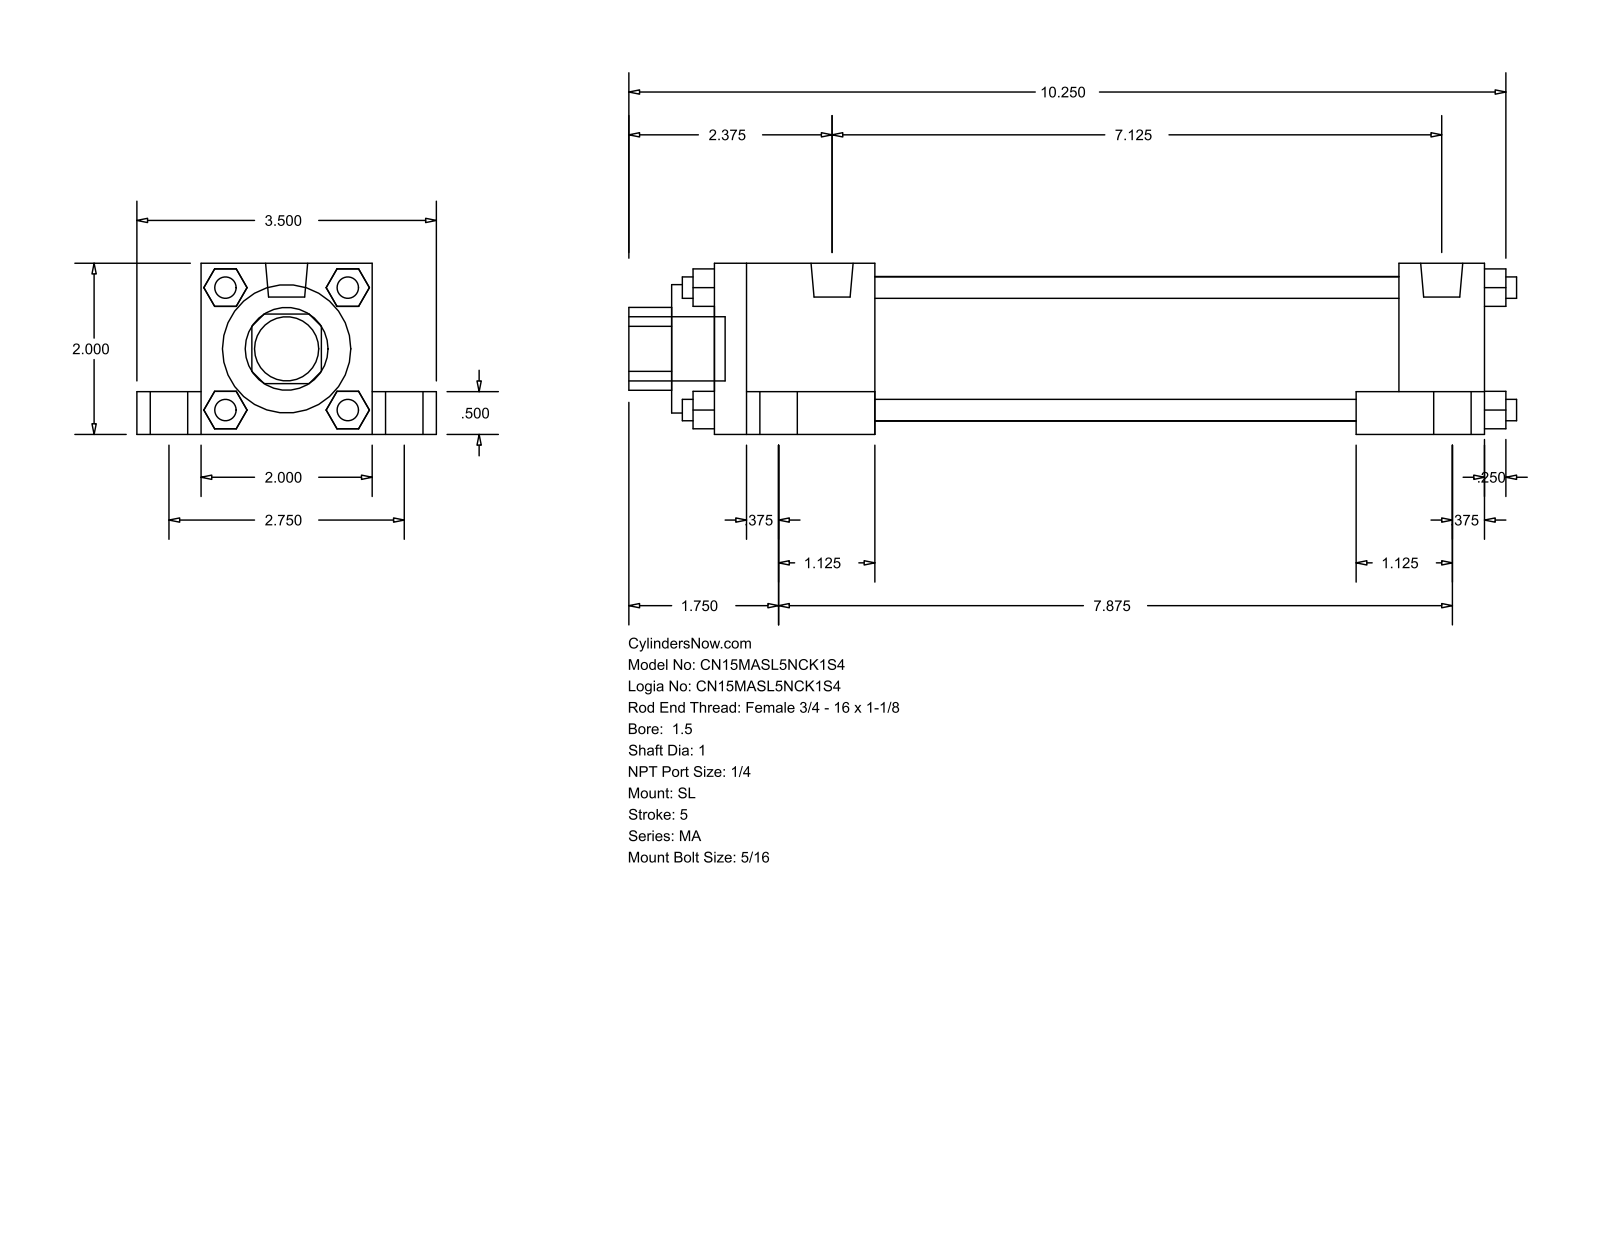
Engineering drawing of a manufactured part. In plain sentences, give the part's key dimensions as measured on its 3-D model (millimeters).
The part is named "MA_SL__0150_1". Its 3-D file was written by "GSSL Pune (CONFIG_CONTROL_DESIGN)". It is 0 solids with 148 faces: 112 planar, 36 cylindrical and 0 other. Overall it measures 263.52 by 88.9 by 50.8 millimeters. Round holes: 1 of diameter 25.4, 1 of diameter 38.1, 1 of diameter 42.93. Round bosses or shafts: 4 of diameter 17.46, 4 of diameter 11.11, 4 of diameter 7.94, 4 of diameter 6.35, 2 of diameter 12.49, 1 of diameter 19.05. Partial cylindrical surfaces (rounded edges, fillets, slot ends): 1 of radius 12.29. The main face-to-face distances are 50.8, 12.7, 19.05, 9.52, 69.85, 38.1, 6.35, 228.6, 25.4, 203.2.
